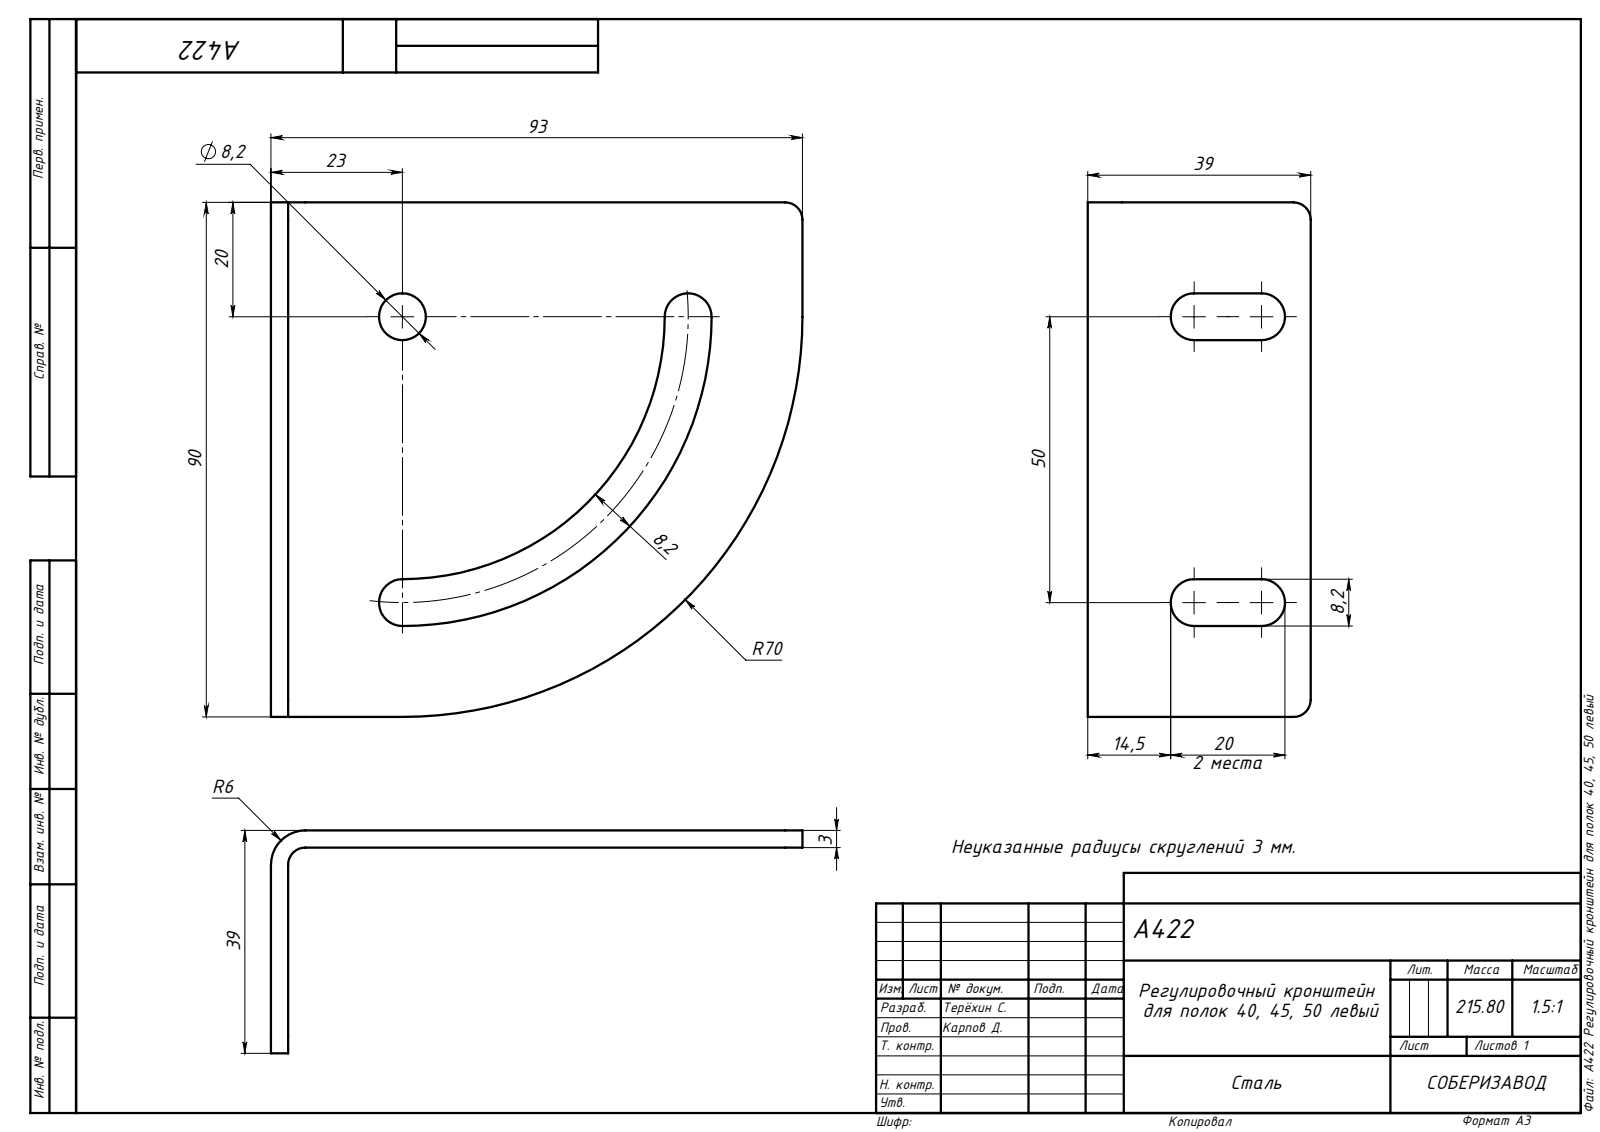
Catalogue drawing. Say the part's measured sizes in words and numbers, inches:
The part is named "A422 Регулировочный кронштейн для полок 40, 45, 50 левый". Its 3-D file was written by "SolidWorks 2020 (AUTOMOTIVE_DESIGN)". It is 1 solid with 32 faces: 16 planar, 16 cylindrical and 0 other. Overall it measures 3.661 by 3.543 by 1.535 inches. Its volume is 1.708 cubic inches and its surface area 32.21 square inches. Round holes: 1 of diameter 0.323. Partial cylindrical surfaces (rounded edges, fillets, slot ends): 6 of radius 0.161, 4 of radius 0.118, 1 of radius 0.236, 1 of radius 1.807, 1 of radius 2.13, 1 of radius 2.756. The main face-to-face distances are 0.118, 1.417, 1.535, 3.543, 0.949, 2.594, 0.626, 2.917, 0.323, 1.969.
